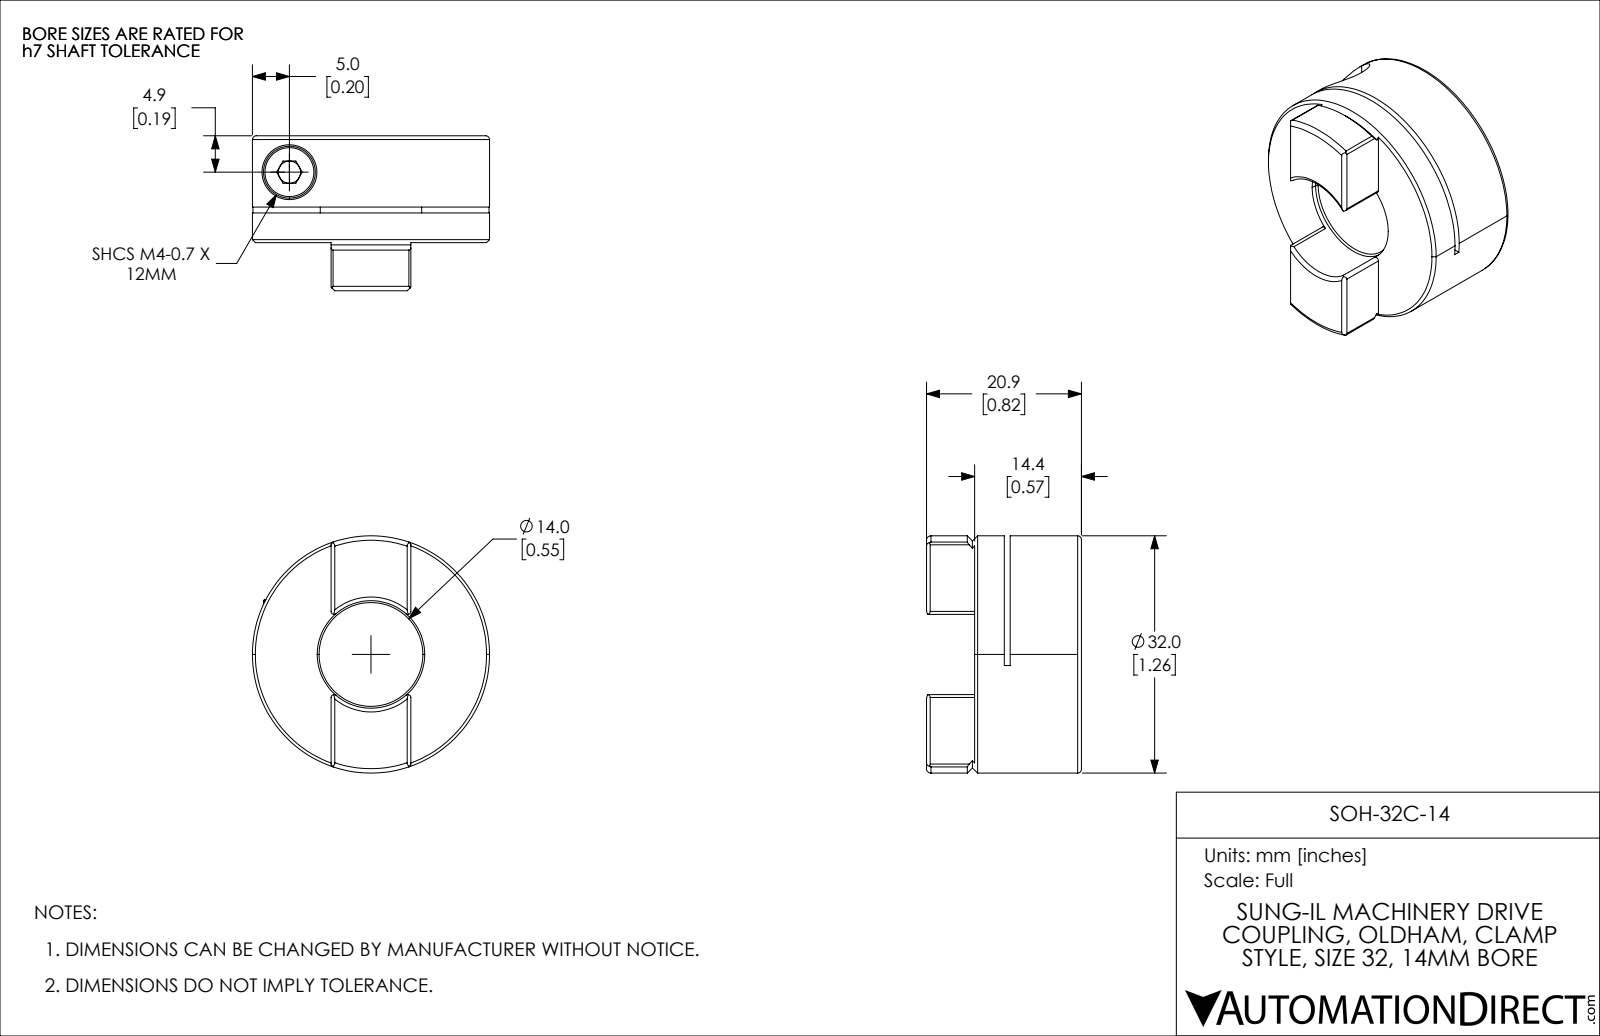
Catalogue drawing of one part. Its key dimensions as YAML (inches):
part_name: "SOH-32C-14"
step_written_by: "SolidWorks 2021 (CONFIG_CONTROL_DESIGN)"
units: inches
bodies: {solids: 2, faces: 96, planar: 38, cylindrical: 33, other: 25}
overall_size: [1.26, 1.26, 0.823]
volume: 0.61
surface_area: 8.196
round_holes:
  - {diameter: 0.118, count: 1}
  - {diameter: 0.13, count: 1}
  - {diameter: 0.173, count: 1}
  - {diameter: 0.291, count: 1}
  - {diameter: 0.551, count: 1}
  - {diameter: 0.571, count: 1}
round_bosses_or_shafts:
  - {diameter: 1.26, count: 1}
  - {diameter: 0.276, count: 1}
  - {diameter: 0.157, count: 1}
partial_cylinders:
  - {radius: 0.016, count: 8}
  - {radius: 0.984, count: 1}
face_to_face_distances: [0.567, 0.157, 0.409, 0.378, 0.031, 0.189, 0.823, 0.445, 0.413, 0.256]
